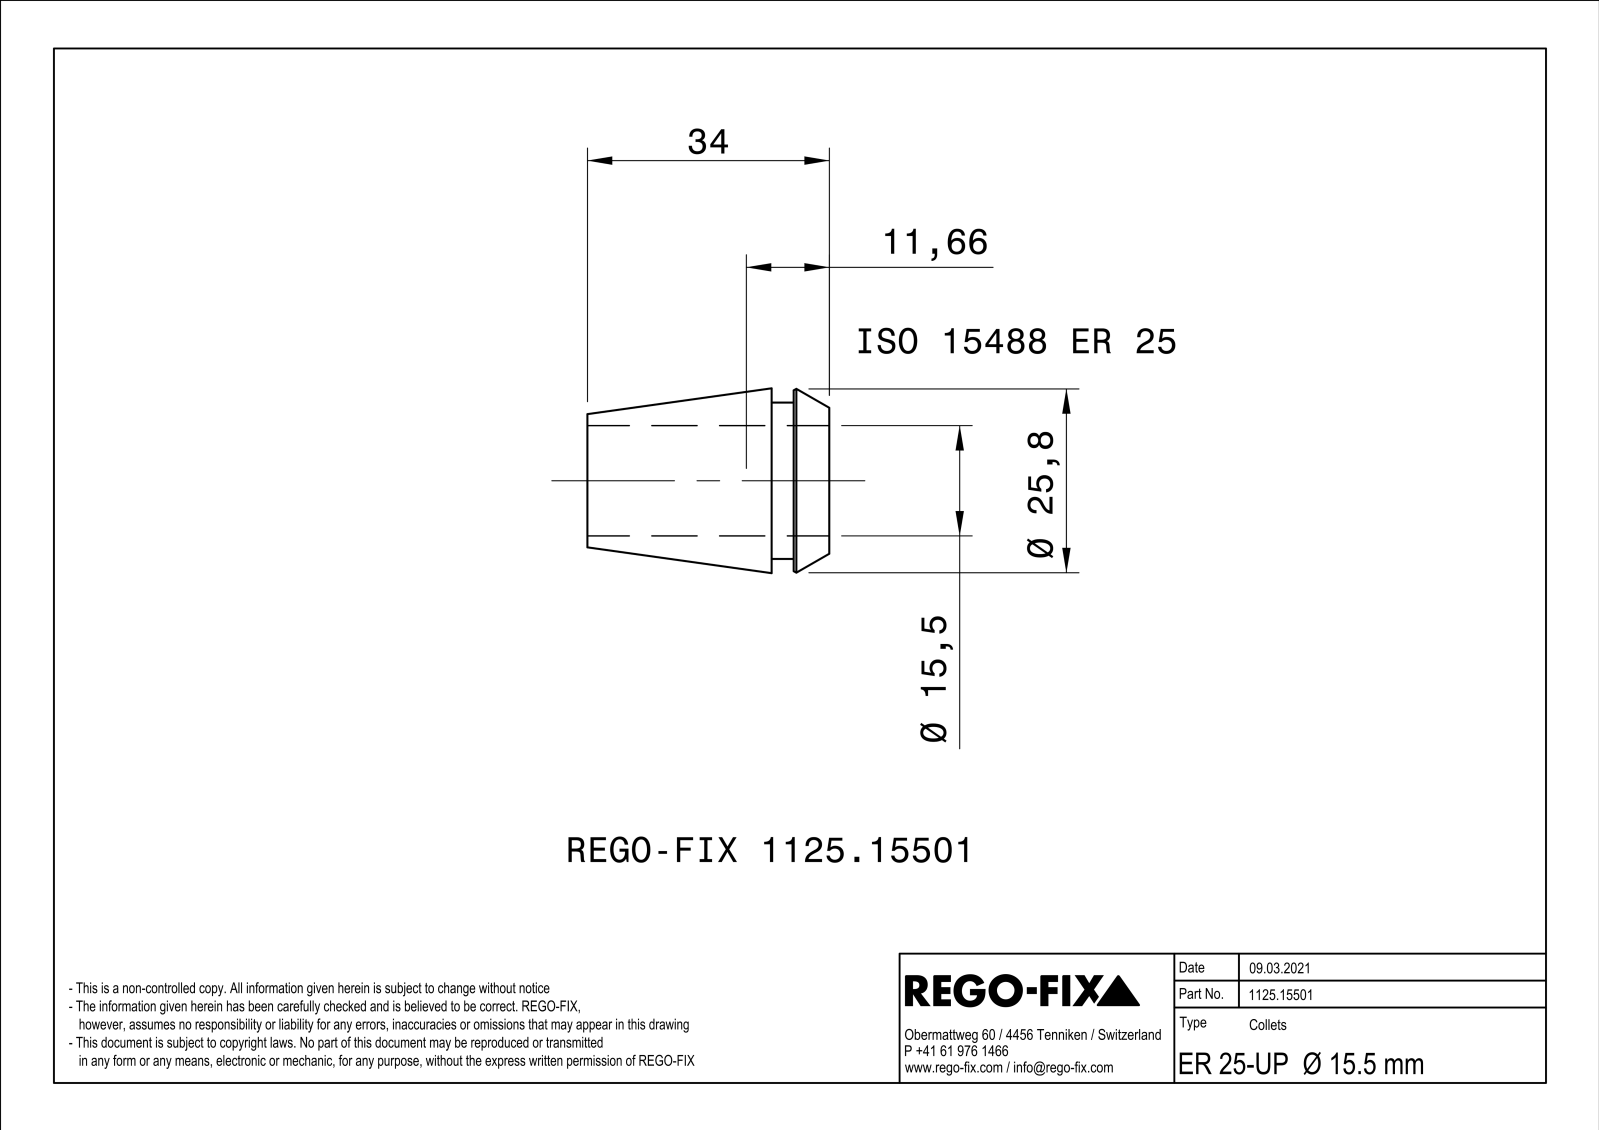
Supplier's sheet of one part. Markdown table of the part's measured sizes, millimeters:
| quantity | value |
| --- | --- |
| part name | NOCUT |
| STEP written by | SIEMENS PLM Software Solid Edge ST10 (AUTOMOTIVE_DESIGN) |
| units | millimeters |
| bodies | 1 solid, 177 faces (72 planar, 25 cylindrical, 80 other) |
| overall size | 34 × 25.99 × 25.99 |
| volume | 5 835 mm³ |
| surface area | 7 173 mm² |
| round holes (diameter × count) | 15.5 × 1 |
| round bosses / shafts (diameter × count) | 22 × 1 |
| partial cylindrical surfaces (radius × count) | 0.4 × 8 |
| main face-to-face distances | 0.8, 8.1, 5, 3.1, 34, 29, 25.9 |
